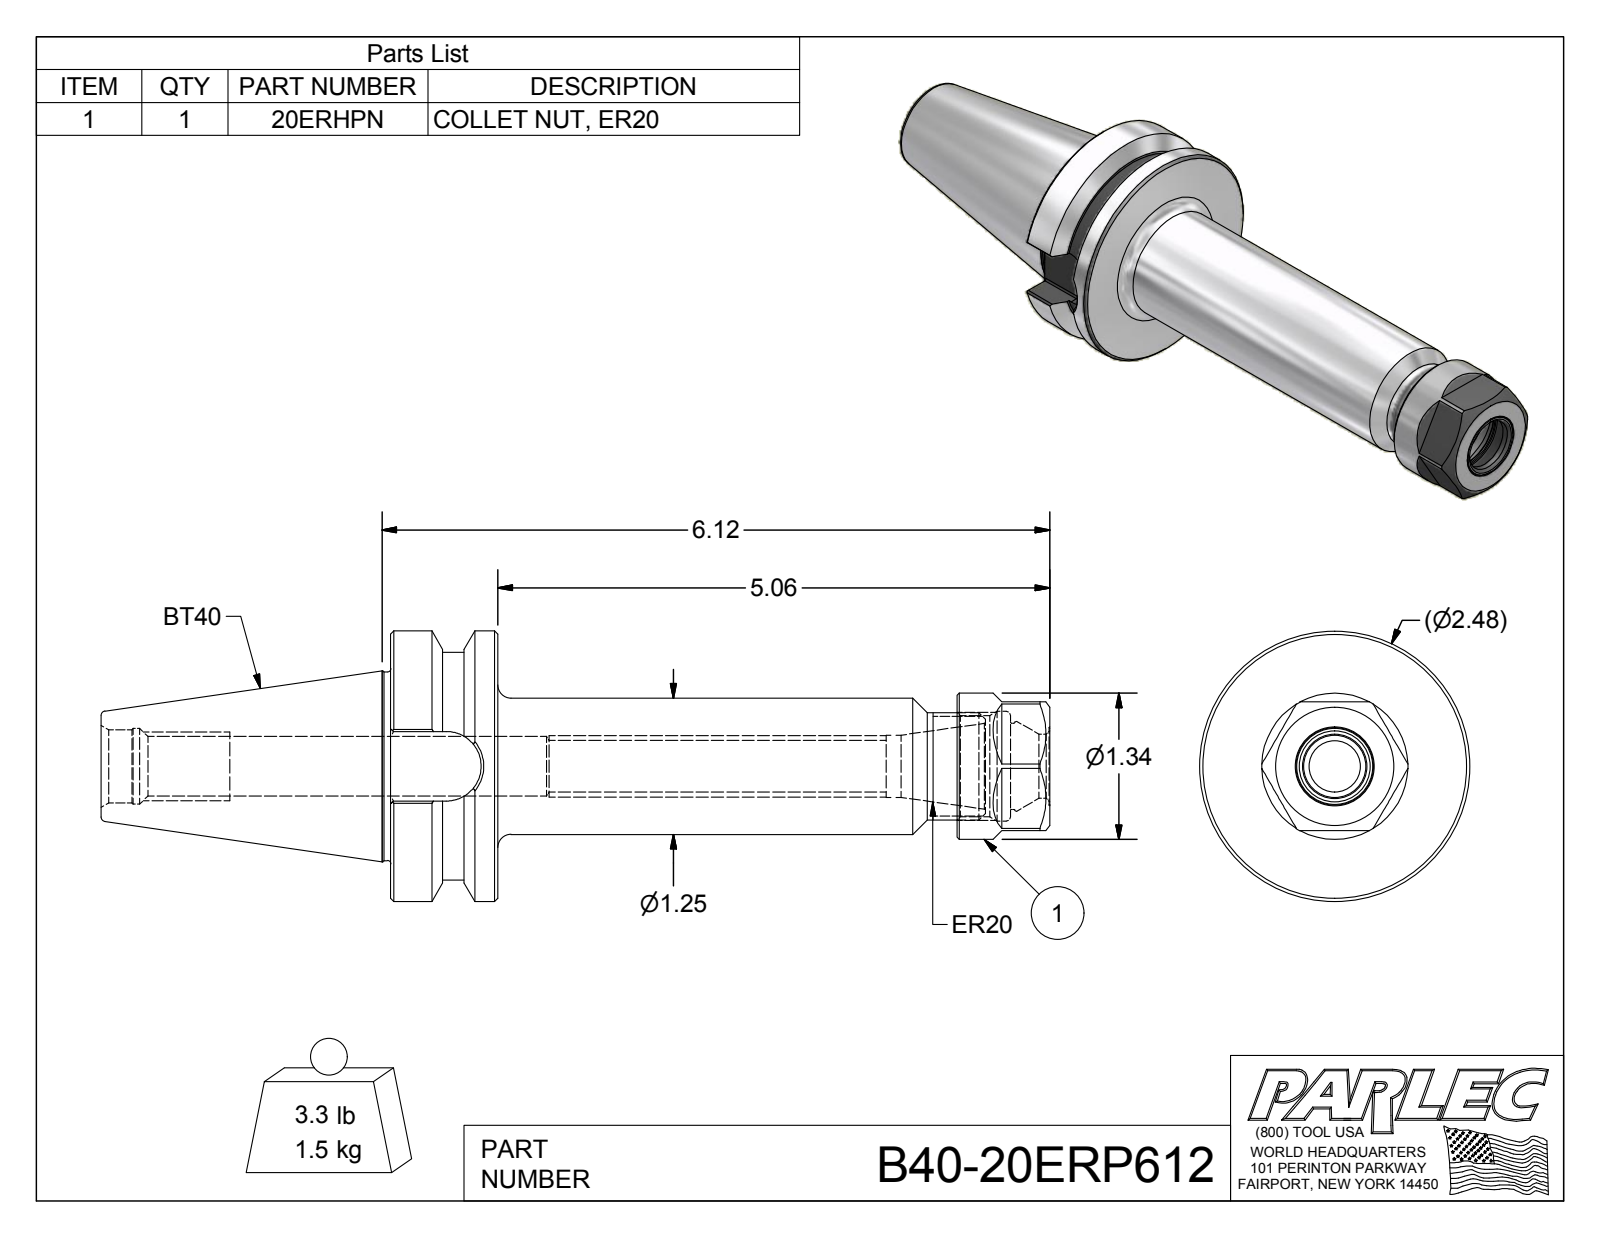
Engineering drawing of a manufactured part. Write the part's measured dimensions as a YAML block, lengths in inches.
part_name: "B40-20ERP612; B40-20ER6-1; 20ERHPN"
step_written_by: "Autodesk Inventor 2012 (AUTOMOTIVE_DESIGN)"
units: inches
bodies: {solids: 2, faces: 104, planar: 40, cylindrical: 28, other: 36}
overall_size: [8.695, 2.48, 2.48]
volume: 12.13
surface_area: 65.74
round_holes:
  - {diameter: 0.472, count: 1}
  - {diameter: 0.545, count: 1}
  - {diameter: 0.57, count: 1}
  - {diameter: 0.587, count: 1}
  - {diameter: 0.67, count: 1}
  - {diameter: 0.694, count: 1}
  - {diameter: 0.79, count: 1}
  - {diameter: 0.926, count: 1}
  - {diameter: 1.005, count: 1}
round_bosses_or_shafts:
  - {diameter: 2.48, count: 1}
  - {diameter: 2.087, count: 1}
  - {diameter: 1.73, count: 1}
  - {diameter: 1.34, count: 1}
  - {diameter: 1.25, count: 1}
  - {diameter: 0.984, count: 1}
partial_cylinders:
  - {radius: 0.02, count: 8}
  - {radius: 0.319, count: 1}
face_to_face_distances: [0.984, 1.18, 5.192, 4.208, 6.042, 5.058, 0.85, 0.272, 0.909, 1.78]
